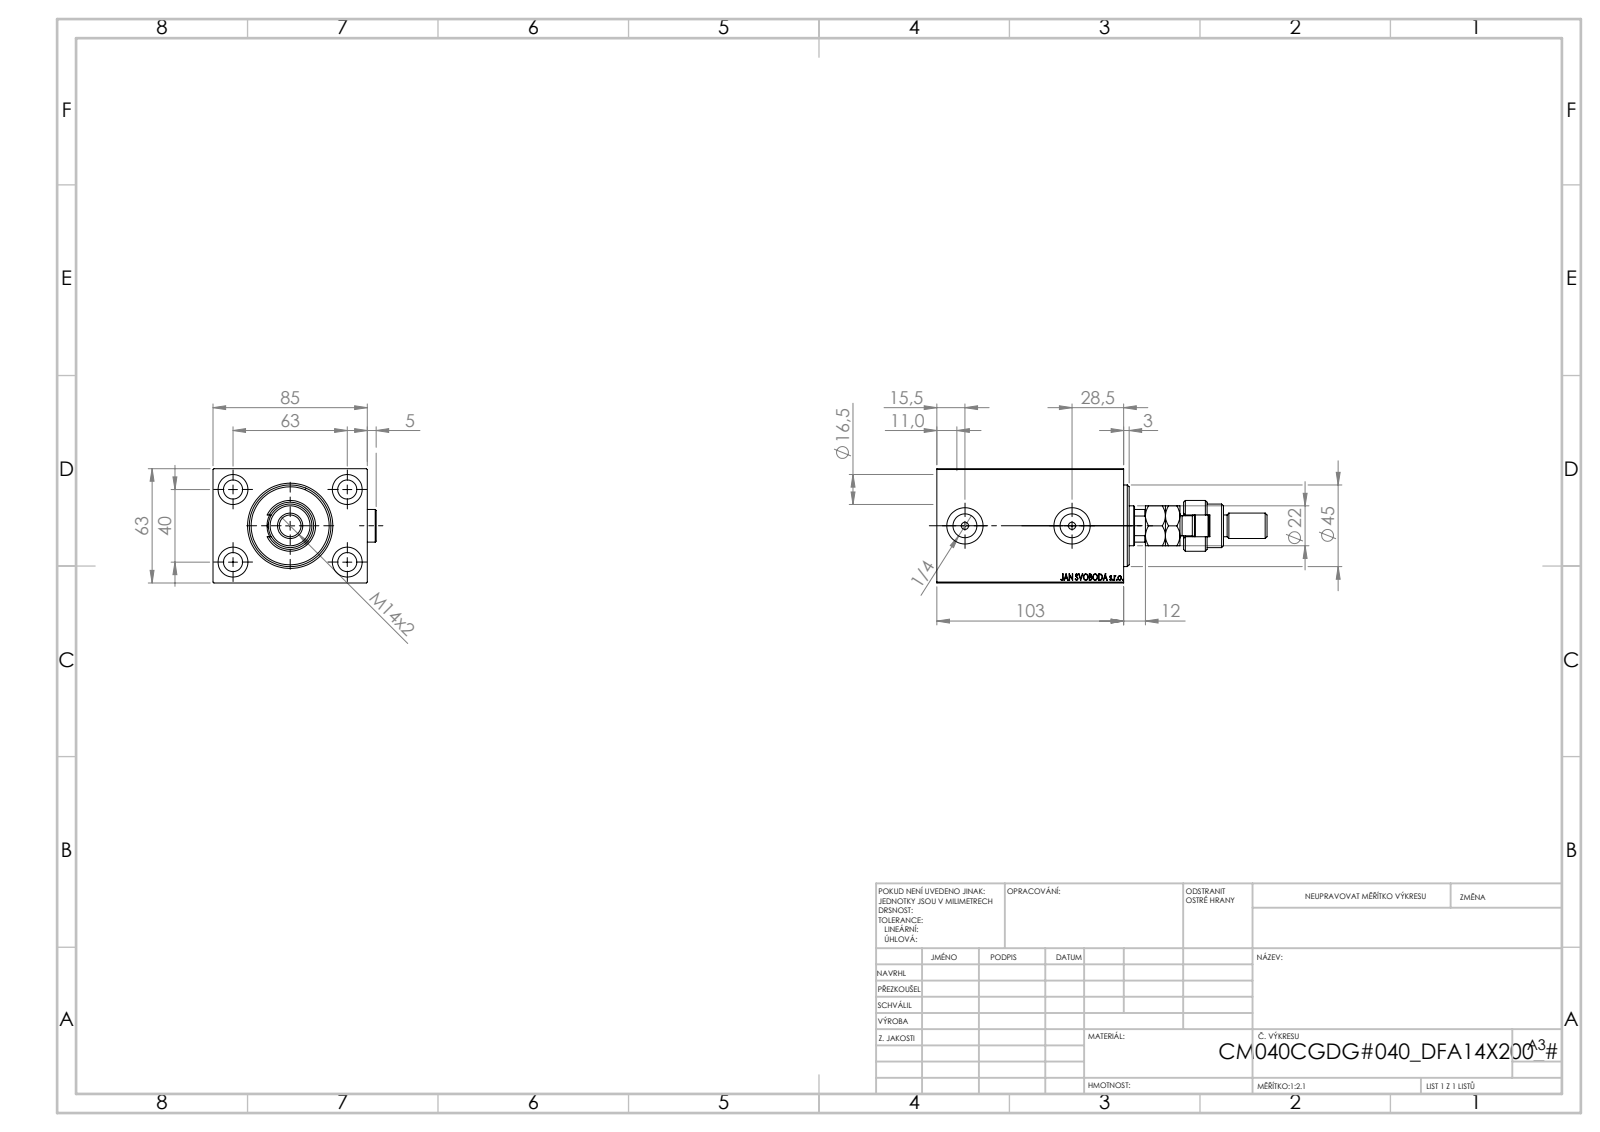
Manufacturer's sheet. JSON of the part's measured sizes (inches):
{"part_name": "FEMALE_PART_FOR_DFA; Zatka_OIL_PORT; V450CM_C_Body; V450CM_C_VCP (+2 more)", "step_written_by": "SolidWorks 2019 (CONFIG_CONTROL_DESIGN)", "units": "inches", "bodies": {"solids": 7, "faces": 1001, "planar": 470, "cylindrical": 89, "other": 442}, "overall_size": [7.165, 3.539, 2.48], "volume_in3": 29.96, "surface_area_in2": 151, "round_holes": [[0.413, 4], [0.65, 4], [0.157, 2], [0.518, 2], [0.787, 2], [0.492, 1], [0.866, 1], [1.004, 1], [1.575, 1], [1.654, 1], [1.772, 1]], "round_bosses_or_shafts": [[0.709, 3], [1.102, 1], [0.945, 1], [0.551, 1], [0.472, 1], [0.433, 1]], "partial_cylinders_radius": [[0.384, 1], [0.413, 1]], "face_to_face_distances": [2.48, 3.346, 0.472, 3.583, 4.055, 1.575, 2.047, 3.11, 3.343, 0.118], "hole_center_spacings": [1.469, 1.575, 2.48, 2.938, 2.323]}
